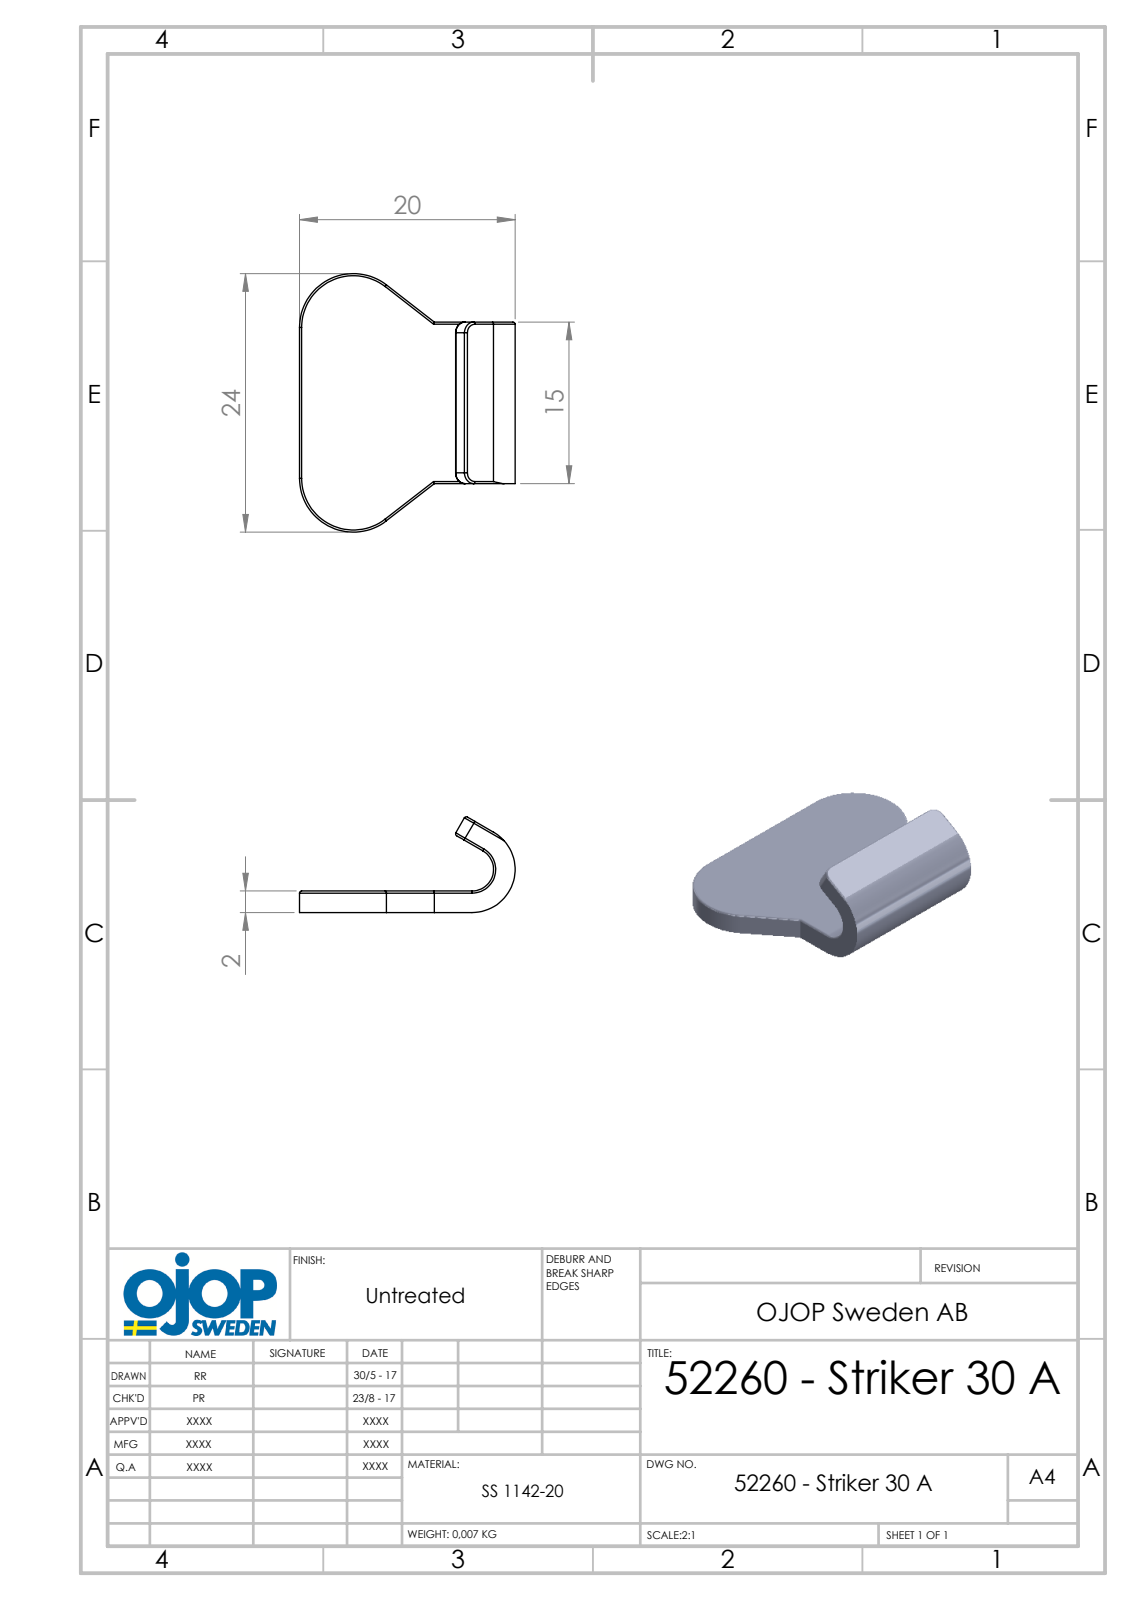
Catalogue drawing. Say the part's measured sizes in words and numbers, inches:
The part is named "52260 - Striker 30 A". Its 3-D file was written by "SolidWorks 2015 (AUTOMOTIVE_DESIGN)". It is 1 solid with 43 faces: 10 planar, 21 cylindrical and 12 other. Overall it measures 0.945 by 0.787 by 0.35 inches. Its volume is 0.058 cubic inches and its surface area 1.744 square inches. Partial cylindrical surfaces (rounded edges, fillets, slot ends): 12 of radius 0.008, 2 of radius 0.039, 2 of radius 0.197, 1 of radius 0.079, 1 of radius 0.157. The main face-to-face distances are 0.079, 0.591.
